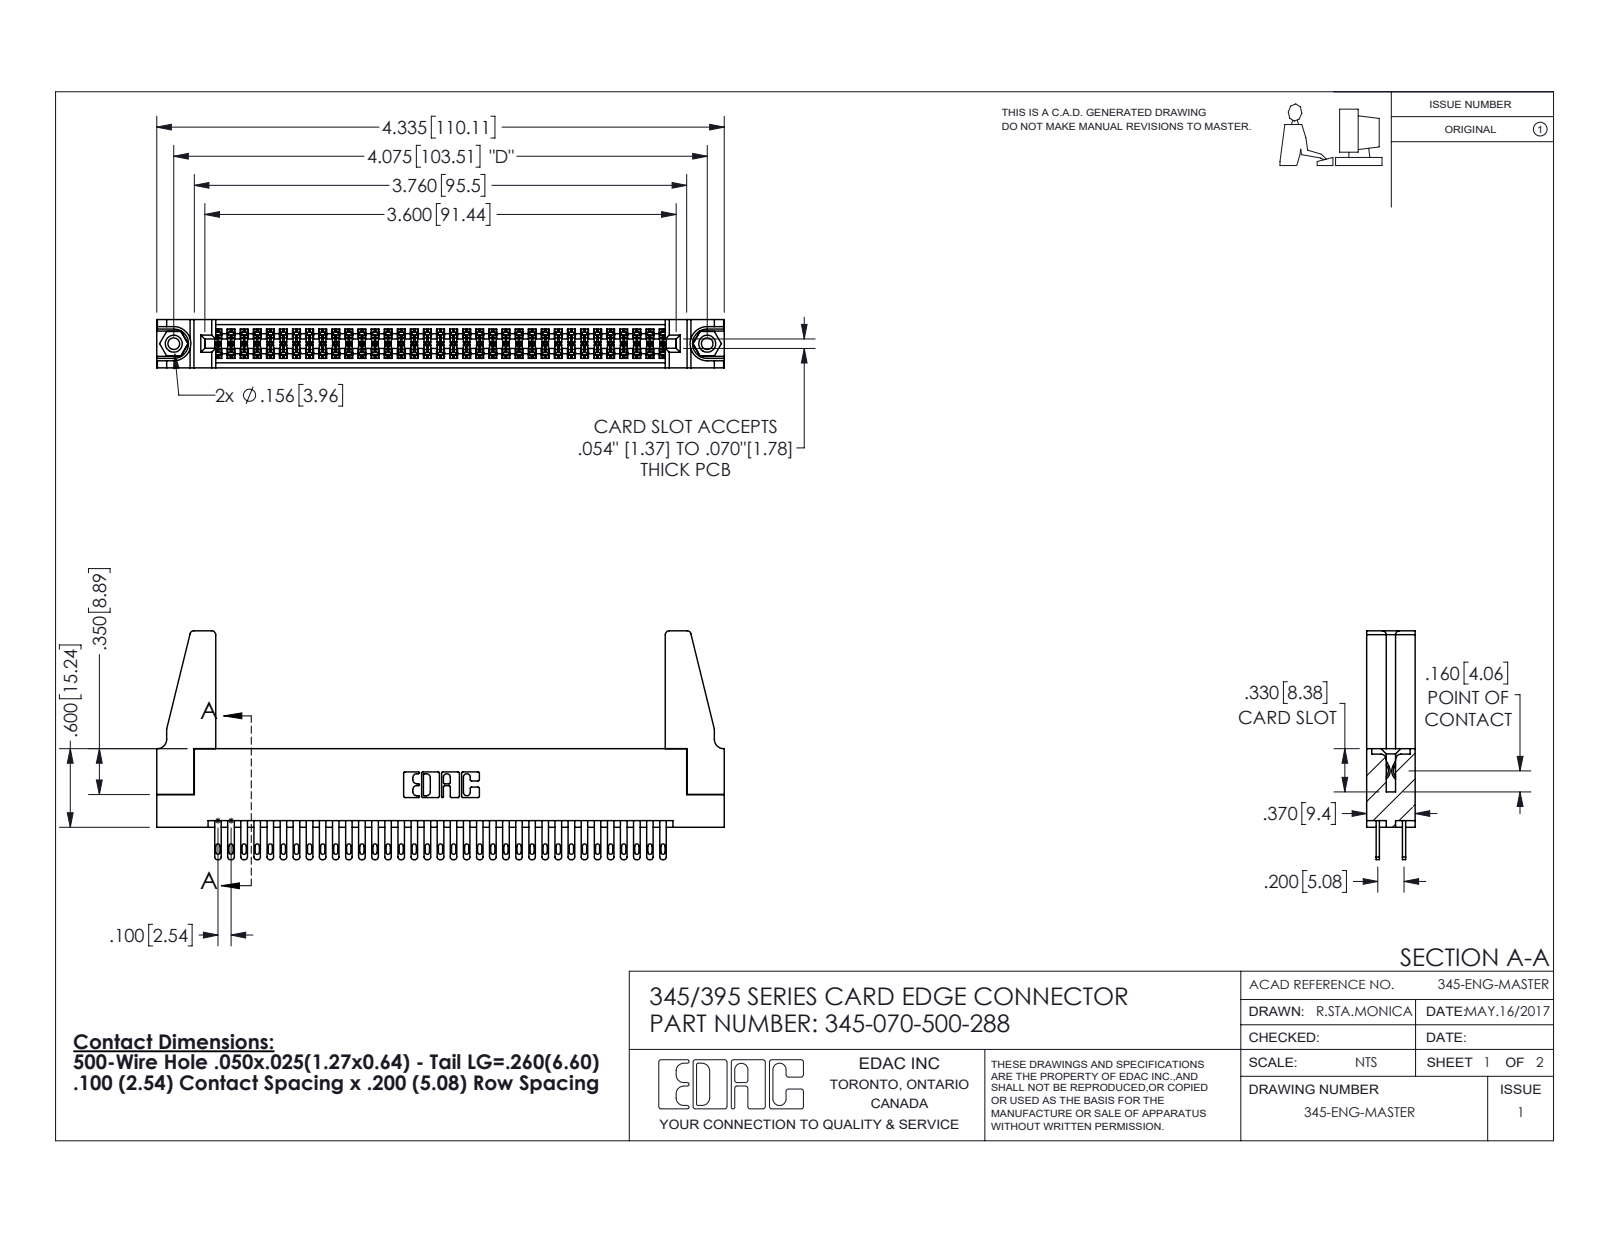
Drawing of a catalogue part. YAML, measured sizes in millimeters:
part_name: "345-070-500-288; 345 Part_Flush Mounting Lugs - 0.156 Dia-TH; 345-250-001_345-250-001-102; 345-220-078_345-220-088 (+1 more)"
step_written_by: "SolidWorks 2016 (CONFIG_CONTROL_DESIGN)"
units: millimeters
bodies: {solids: 75, faces: 3470, planar: 2042, cylindrical: 1412, other: 16}
overall_size: [110.1, 44.4, 9.4]
volume: 14100
surface_area: 19740
round_holes:
  - {diameter: 2.3, count: 2}
  - {diameter: 3.2, count: 2}
  - {diameter: 4, count: 2}
  - {diameter: 1.6, count: 1}
round_bosses_or_shafts:
  - {diameter: 3.9, count: 2}
partial_cylinders:
  - {radius: 0.2, count: 105}
  - {radius: 0.4, count: 70}
  - {radius: 0.5, count: 70}
  - {radius: 0.3, count: 22}
  - {radius: 0.8, count: 8}
  - {radius: 0.2, count: 6}
  - {radius: 0.8, count: 6}
  - {radius: 0.7, count: 3}
face_to_face_distances: [1.8, 7.6, 5.1, 9.4, 2.5, 6.9, 0.6, 5.7, 4.4, 3.8]
hole_center_spacings: [6.9, 97.5, 103.5]
